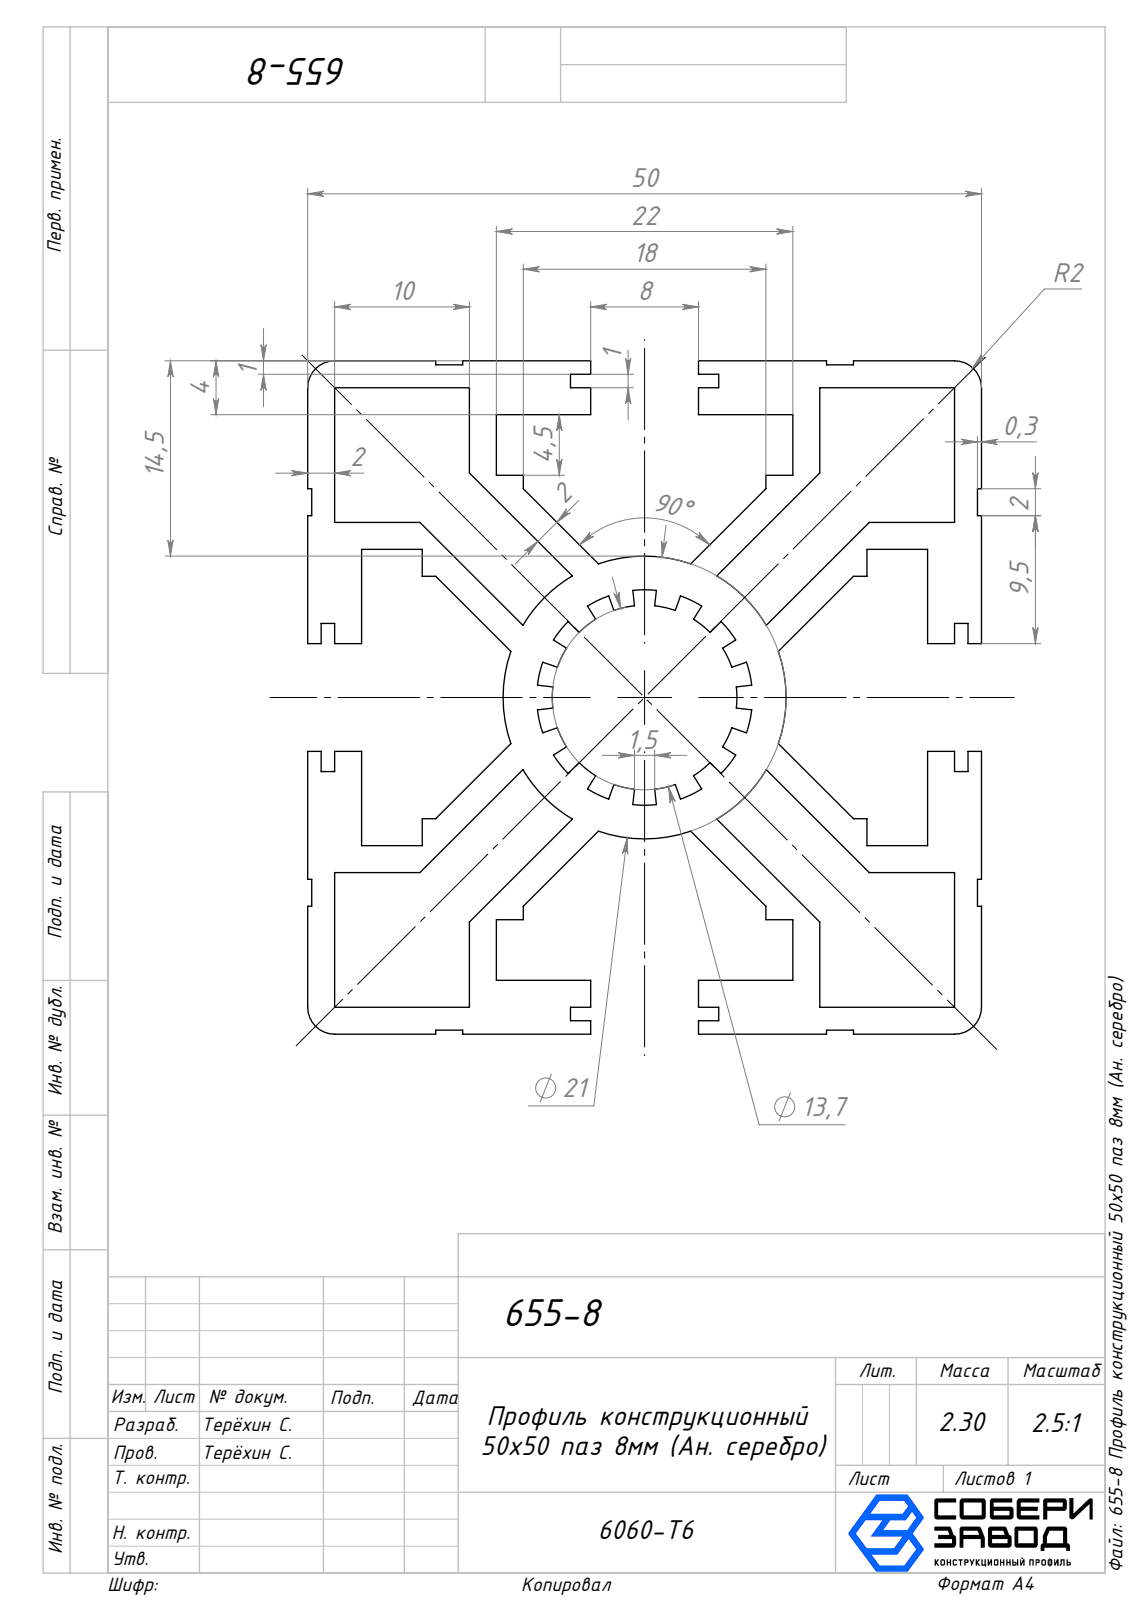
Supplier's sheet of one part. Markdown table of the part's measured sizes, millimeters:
| quantity | value |
| --- | --- |
| part name | 655-8 Профиль конструкционный 50х50 паз 8мм (Ан. серебро)_00; 655-8 Профиль конструкционный 50х50 паз 8мм (Ан. серебро) |
| STEP written by | SolidWorks 2026 (CONFIG_CONTROL_DESIGN) |
| units | millimeters |
| bodies | 1 solid, 215 faces (174 planar, 41 cylindrical, 0 other) |
| overall size | 1000 × 50 × 50 |
| volume | 850 676 mm³ |
| surface area | 750 890 mm² |
| partial cylindrical surfaces (radius × count) | 2 × 4, 6.85 × 1, 8 × 1, 10.5 × 1 |
| main face-to-face distances | 2, 46, 48, 12, 34, 36, 10, 50, 7.2, 8 |
